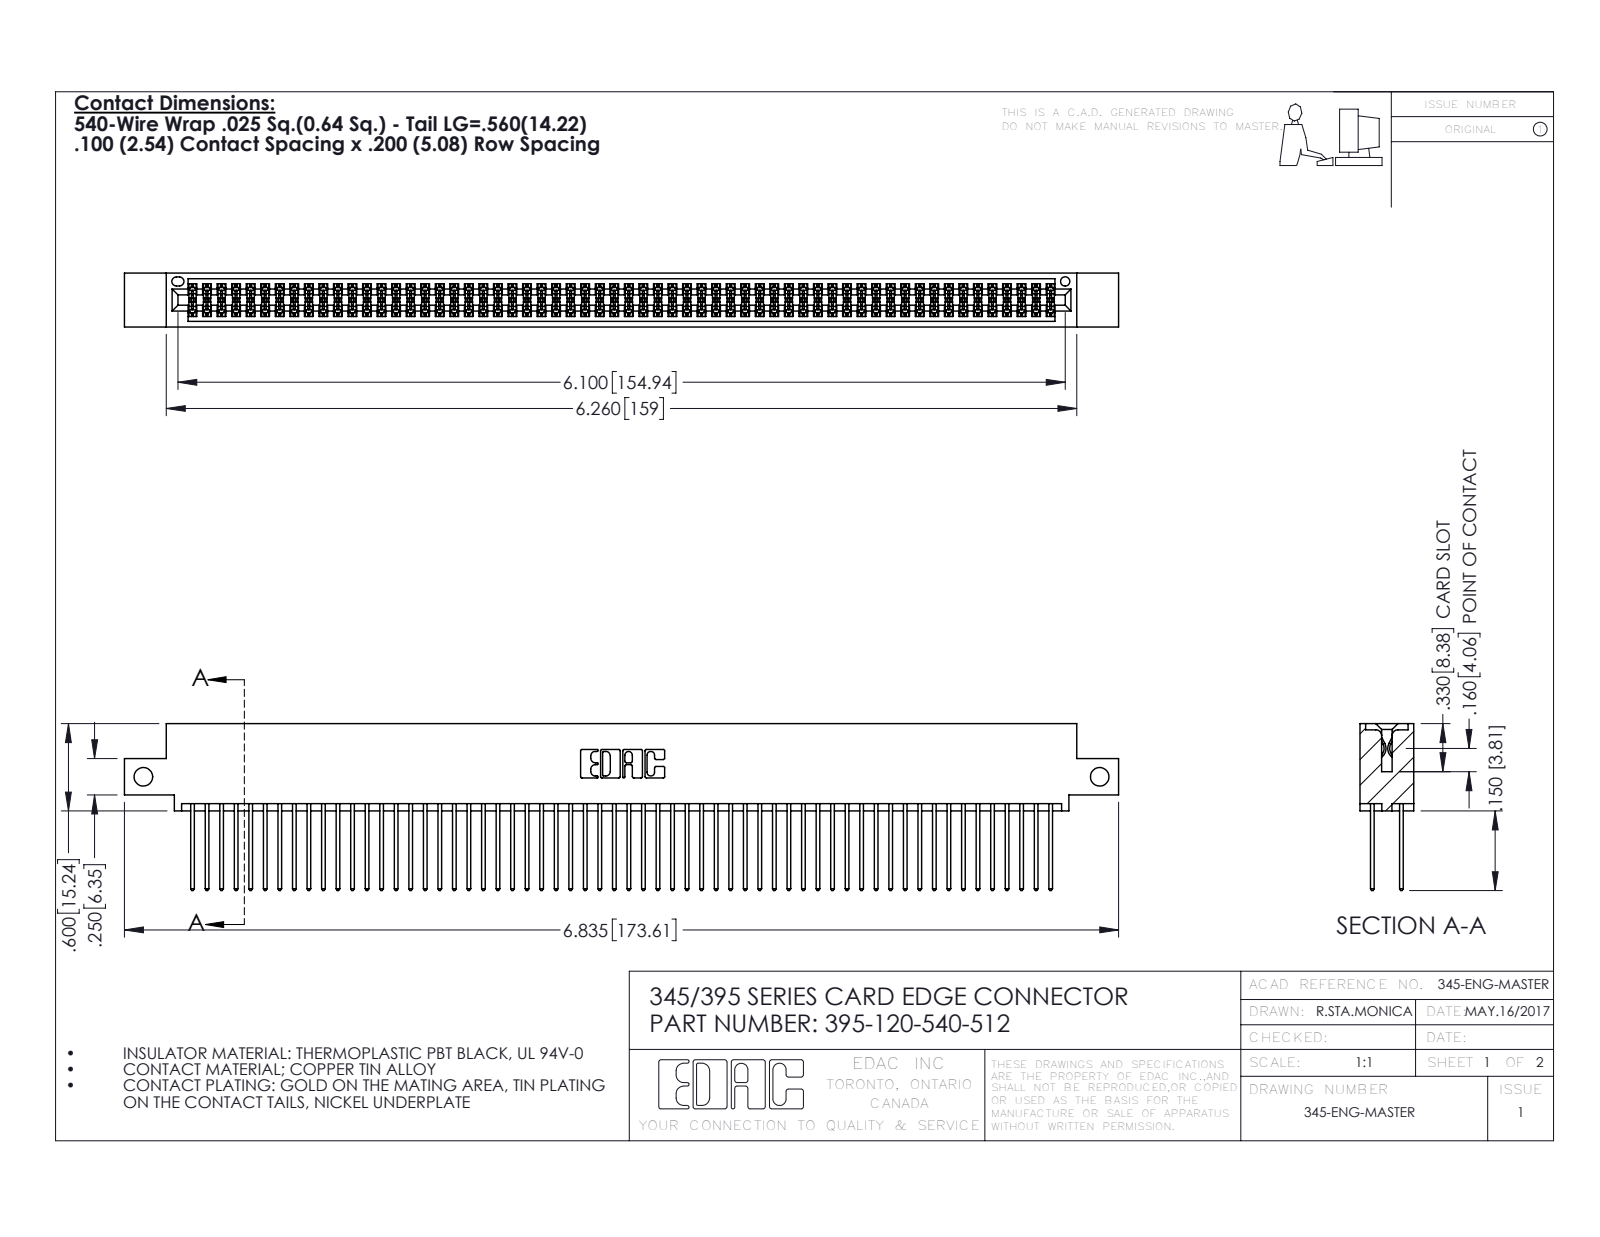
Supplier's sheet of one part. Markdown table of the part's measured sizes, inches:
| quantity | value |
| --- | --- |
| part name | 395-120-540-512; 345 Part_0.110 Offset - Side Mount; 345-292-001_345-293-140 |
| STEP written by | SolidWorks 2016 (CONFIG_CONTROL_DESIGN) |
| units | inches |
| bodies | 121 solids, 6130 faces (4044 planar, 2086 cylindrical, 0 other) |
| overall size | 6.835 × 1.147 × 0.37 |
| volume | 1.057 in³ |
| surface area | 43.44 in² |
| round holes (diameter × count) | 0.128 × 2, 0.064 × 1 |
| partial cylindrical surfaces (radius × count) | 0.006 × 180, 0.01 × 120, 0.01 × 22, 0.007 × 6, 0.031 × 6, 0.026 × 3, 0.014 × 2, 0.019 × 2 |
| main face-to-face distances | 0.072, 0.298, 0.2, 0.098, 0.272, 0.025, 0.225, 0.37, 0.175, 0.149 |
| hole center spacings | 6.575 |
